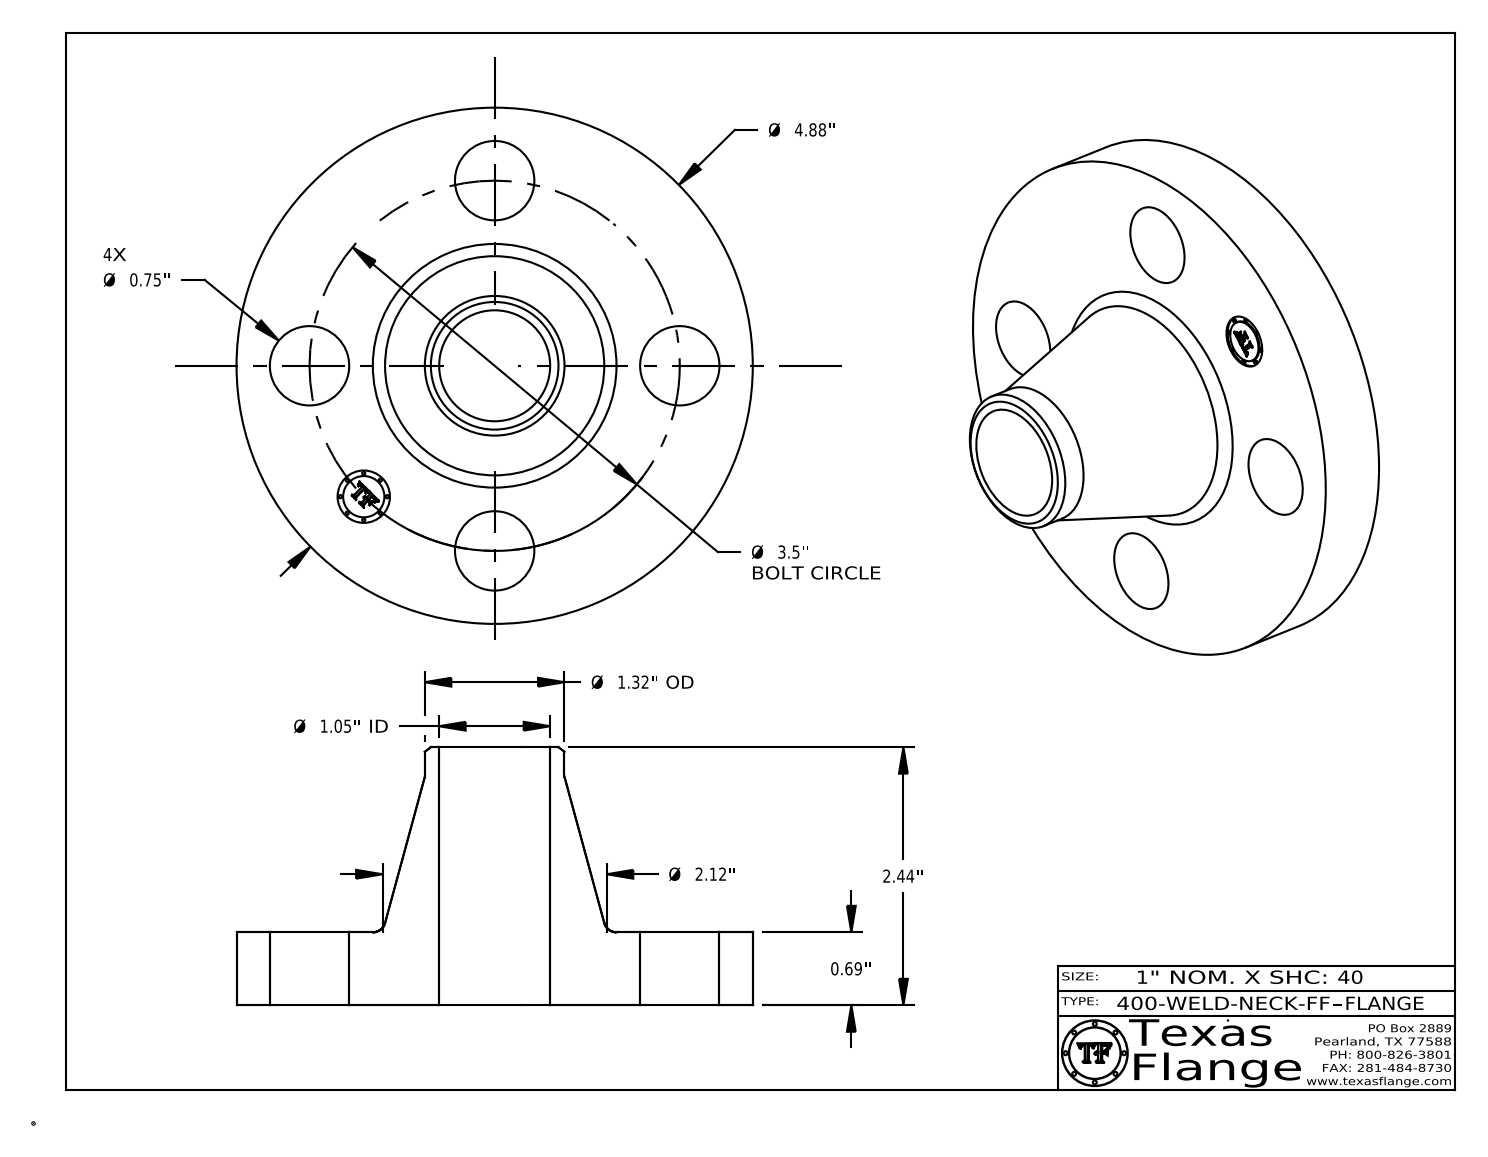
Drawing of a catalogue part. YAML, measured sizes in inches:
part_name: "400-WELD-NECK-FF"
step_written_by: "CATIA V5 STEP AP214 (AUTOMOTIVE_DESIGN)"
units: inches
bodies: {solids: 1, faces: 408, planar: 368, cylindrical: 34, other: 6}
overall_size: [4.88, 4.88, 2.44]
volume: 13.44
surface_area: 64.3
round_holes:
  - {diameter: 0.75, count: 4}
  - {diameter: 0.495, count: 1}
  - {diameter: 1.049, count: 1}
round_bosses_or_shafts:
  - {diameter: 0.03, count: 8}
  - {diameter: 4.88, count: 1}
  - {diameter: 1.32, count: 1}
  - {diameter: 0.39, count: 1}
face_to_face_distances: [0.69, 2.44, 1.75, 0.015, 0.675, 1.765, 0.148, 0.145, 0.027, 0.096]
hole_center_spacings: [1.75, 2.475, 1.339, 3.233, 3.5]
